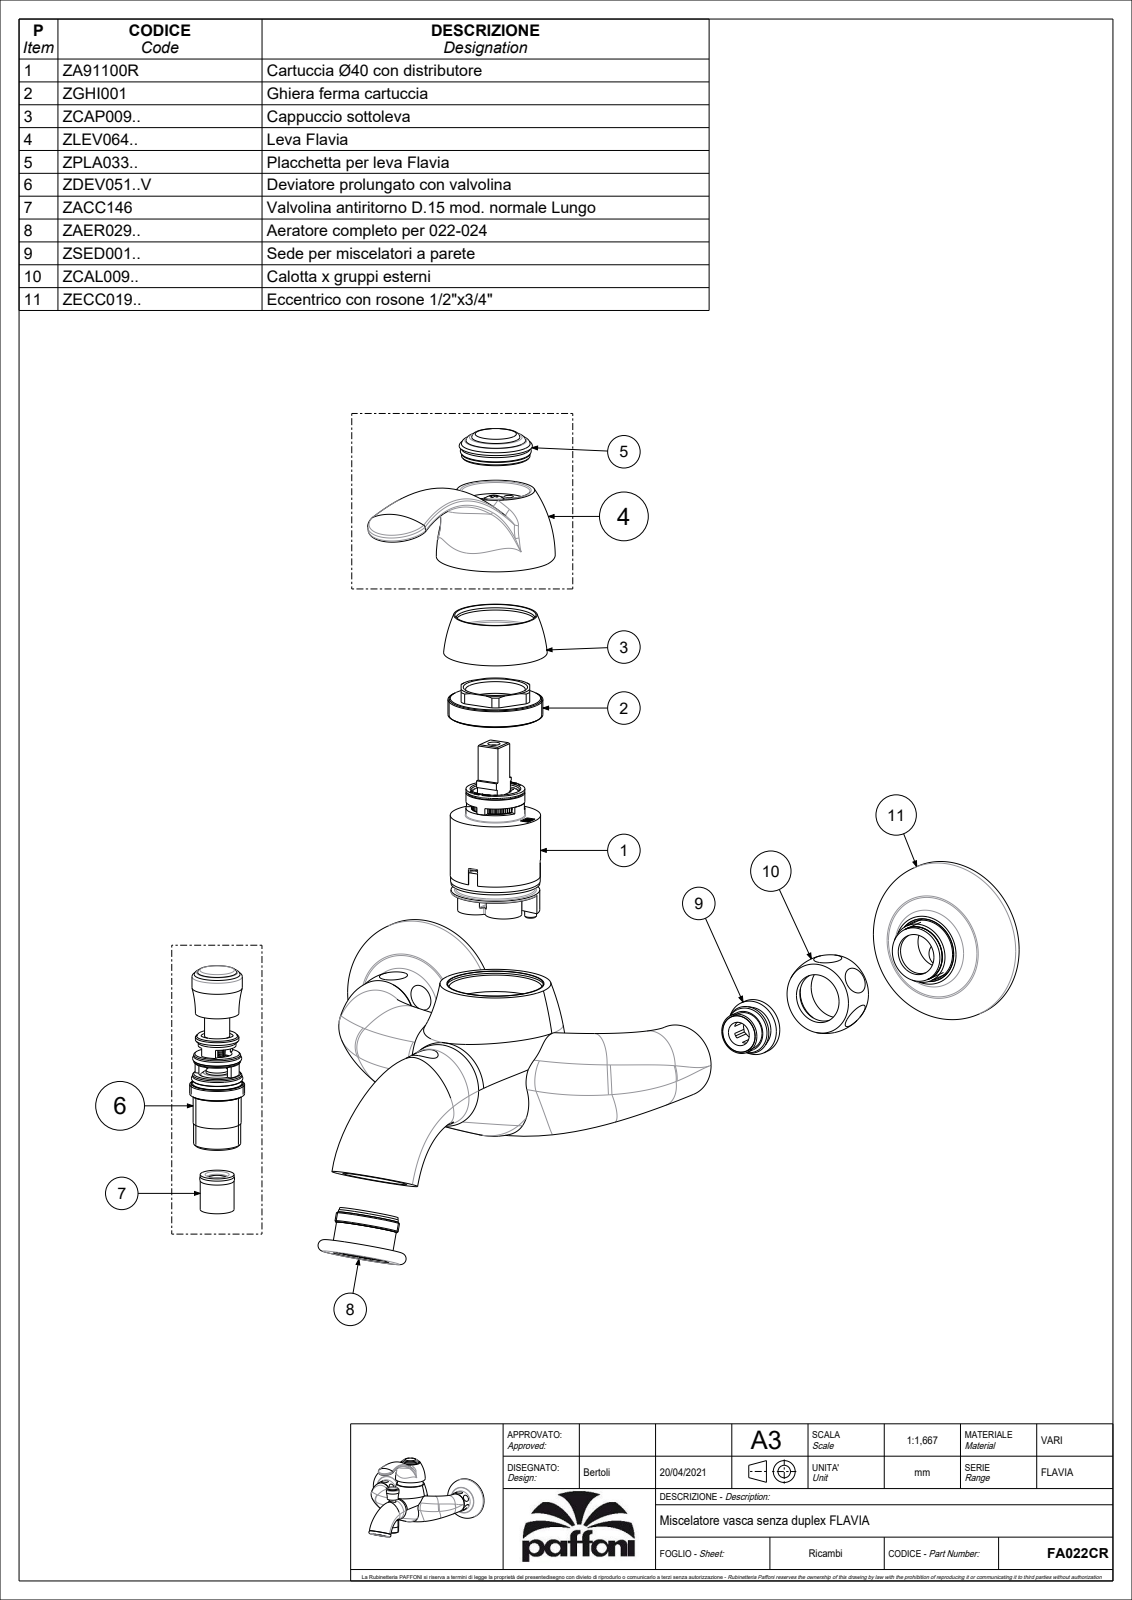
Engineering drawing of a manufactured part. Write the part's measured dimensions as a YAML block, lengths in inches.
part_name: "FA022CR"
step_written_by: "CREO PARAMETRIC BY PTC INC, 2020044 (CONFIG_CONTROL_DESIGN)"
units: inches
bodies: {solids: 2, faces: 2376, planar: 1310, cylindrical: 629, other: 437}
overall_size: [8.661, 7.572, 4.944]
volume: 25.33
surface_area: 221.4
round_holes:
  - {diameter: 0.02, count: 91}
  - {diameter: 0.315, count: 4}
  - {diameter: 0.709, count: 3}
  - {diameter: 0.13, count: 2}
  - {diameter: 0.157, count: 2}
  - {diameter: 0.197, count: 2}
  - {diameter: 0.247, count: 2}
  - {diameter: 0.413, count: 2}
  - {diameter: 0.433, count: 2}
  - {diameter: 0.472, count: 2}
  - {diameter: 0.846, count: 2}
  - {diameter: 0.949, count: 2}
round_bosses_or_shafts:
  - {diameter: 0.945, count: 4}
  - {diameter: 2.756, count: 2}
  - {diameter: 1.108, count: 2}
  - {diameter: 0.626, count: 2}
  - {diameter: 0.37, count: 2}
  - {diameter: 1.555, count: 1}
  - {diameter: 1.543, count: 1}
  - {diameter: 1.528, count: 1}
partial_cylinders:
  - {radius: 0.02, count: 63}
  - {radius: 0.008, count: 24}
  - {radius: 0.012, count: 8}
  - {radius: 0.059, count: 8}
  - {radius: 0.217, count: 2}
  - {radius: 0.295, count: 2}
  - {radius: 0.177, count: 1}
  - {radius: 0.276, count: 1}
face_to_face_distances: [0.039, 0.098, 1.26, 0.118, 3.028, 1.555, 0.256, 0.315, 0.354, 1.654]
hole_center_spacings: [0.15, 0.226, 0.075, 0.301, 0.078, 0.199, 0.225, 0.376]
